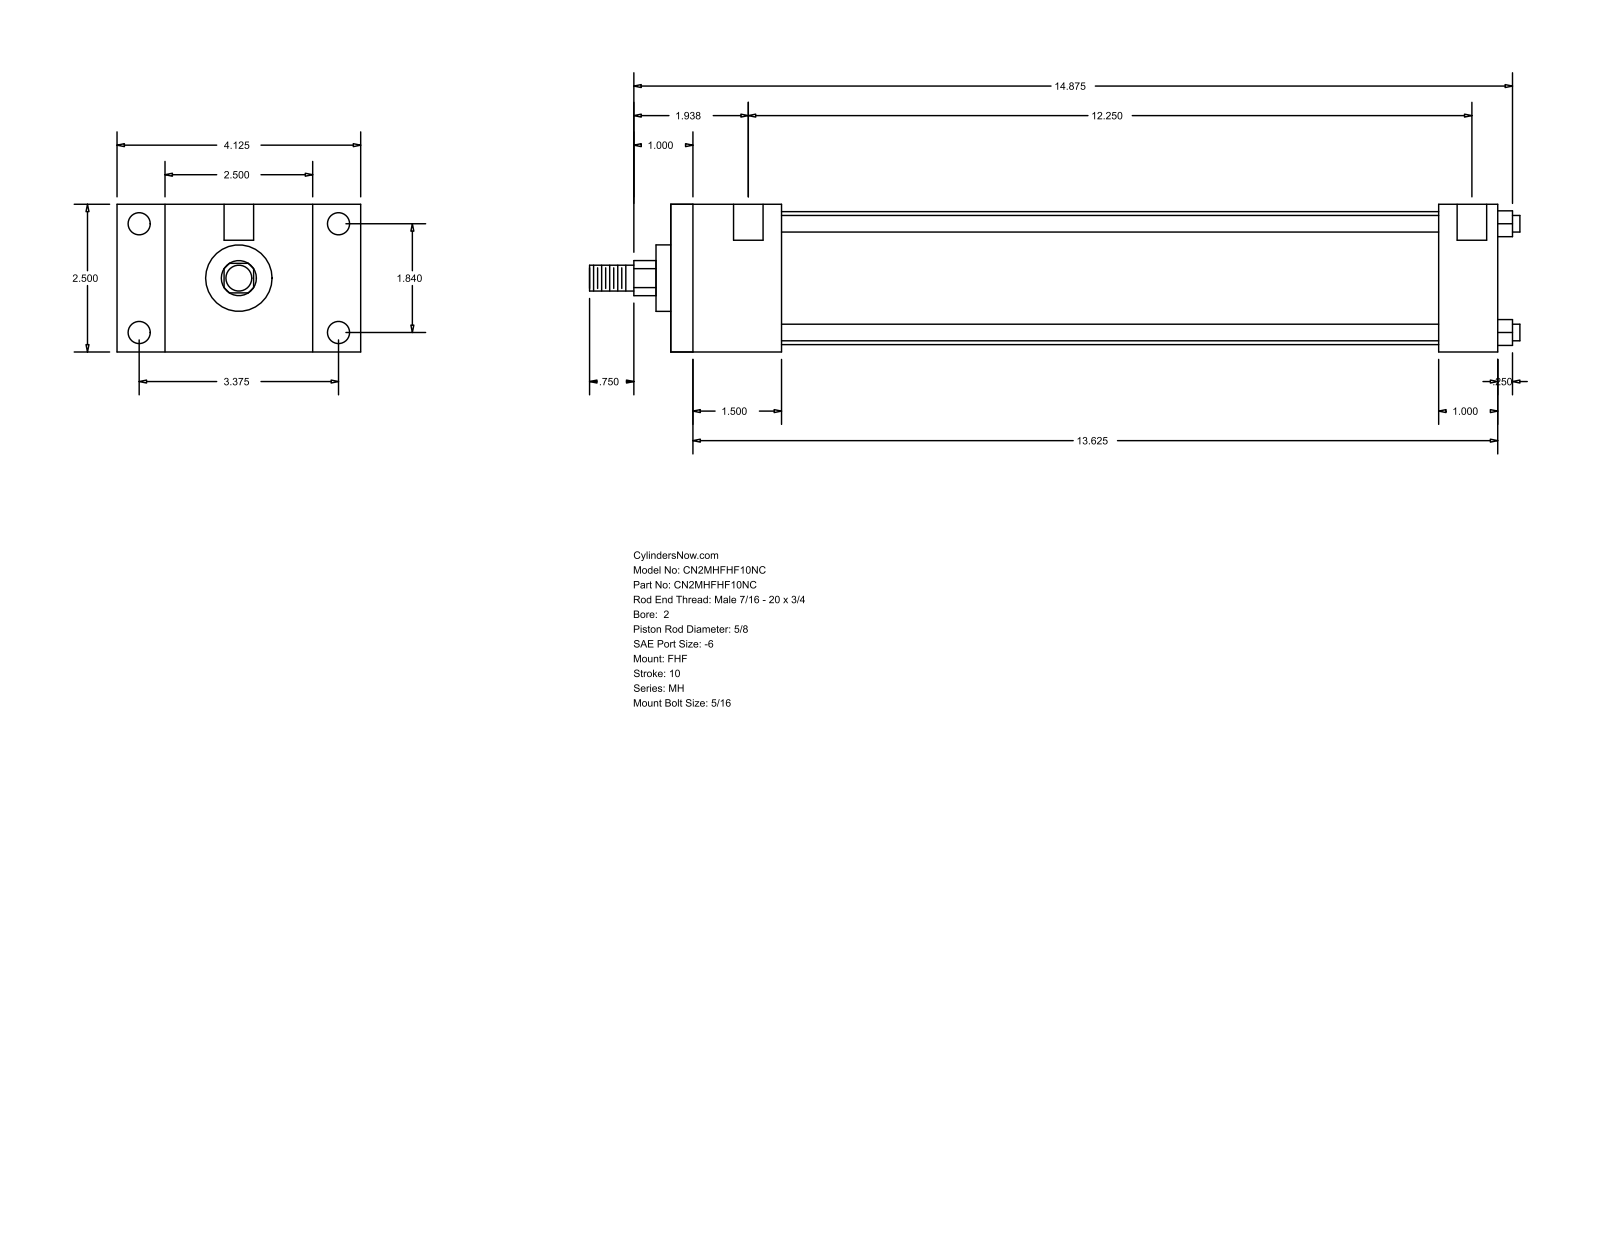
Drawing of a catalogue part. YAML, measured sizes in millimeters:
part_name: "MH_FHF__0200_0.625"
step_written_by: "GSSL Pune (CONFIG_CONTROL_DESIGN)"
units: millimeters
bodies: {solids: 0, faces: 88, planar: 60, cylindrical: 28, other: 0}
overall_size: [400.05, 104.78, 63.5]
round_holes:
  - {diameter: 5.56, count: 4}
  - {diameter: 9.53, count: 4}
  - {diameter: 12.7, count: 2}
round_bosses_or_shafts:
  - {diameter: 7.14, count: 4}
  - {diameter: 57.15, count: 1}
  - {diameter: 28.57, count: 1}
  - {diameter: 15.88, count: 1}
  - {diameter: 11.11, count: 1}
partial_cylinders:
  - {radius: 7.54, count: 1}
face_to_face_distances: [63.5, 47.62, 355.6, 307.98, 20.64, 84.14, 104.78, 330.19, 282.57, 25.41]
hole_center_spacings: [46.74, 85.72, 97.63, 319.09, 3.18, 4.76, 311.15, 314.33]
